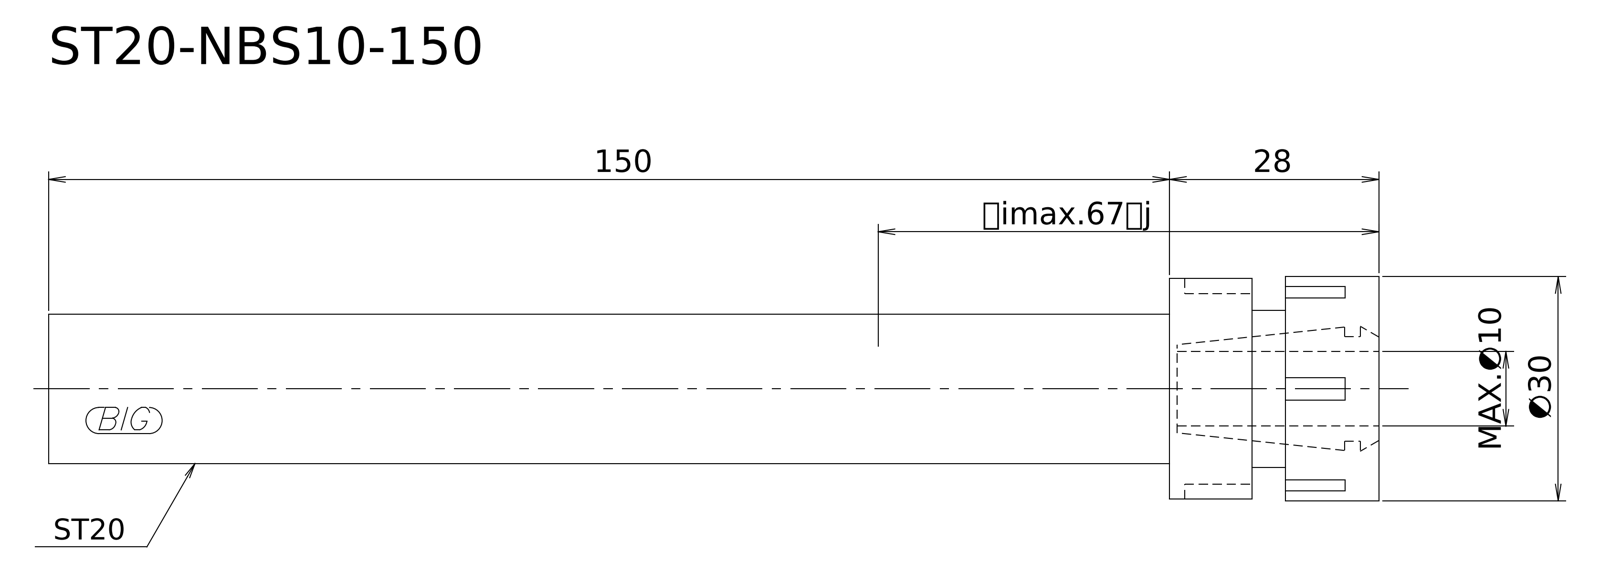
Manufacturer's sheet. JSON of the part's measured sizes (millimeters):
{"step_written_by": "Kubotek KeyCreator V8.5.1 (14335) (CONFIG_CONTROL_DESIGN)", "units": "millimeters", "bodies": {"solids": 1, "faces": 9, "planar": 5, "cylindrical": 4, "other": 0}, "overall_size": [178, 30, 30], "volume_mm3": 65037, "surface_area_mm2": 14007, "round_bosses_or_shafts": [[30, 1], [29.5, 1], [21, 1], [20, 1]], "face_to_face_distances": [28, 12.5, 15.5, 17, 4.5, 11, 178, 165.5, 161, 150]}
